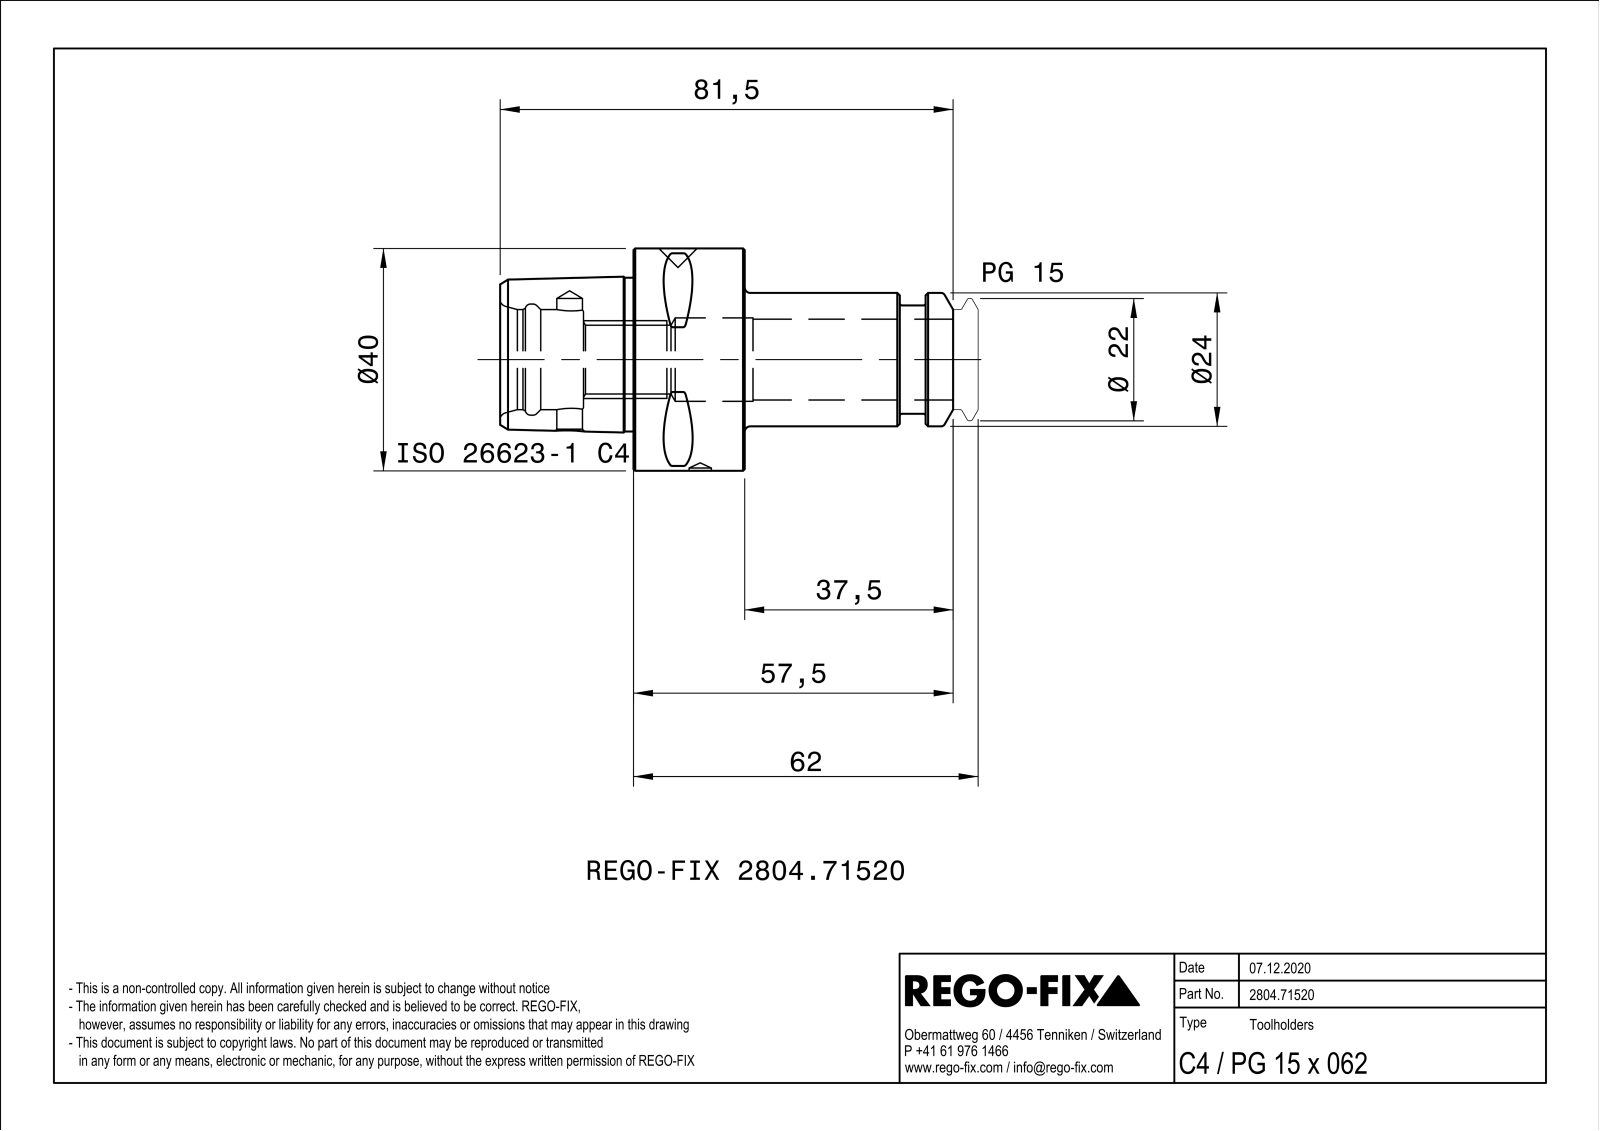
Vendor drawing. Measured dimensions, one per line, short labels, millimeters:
name: NOCUT
written by: SIEMENS PLM Software Solid Edge ST10 (AUTOMOTIVE_DESIGN)
unit: mm
bodies: 1 solid, 112 faces (23 planar, 22 cylindrical, 67 other)
size: 81.5 × 40 × 40
volume: 39 845 mm³; area: 13 614 mm²
holes: 1× ⌀4, 1× ⌀4.6, 1× ⌀12.38, 1× ⌀15, 1× ⌀18, 1× ⌀20
bosses: 1× ⌀40, 1× ⌀24, 1× ⌀19.5
rounds: 8× R0.5, 1× R3
face distances: 20, 44, 24, 15.52, 27.9, 47.9, 71.9, 4.6, 32.5, 52.5
hole spacings: 23.5
